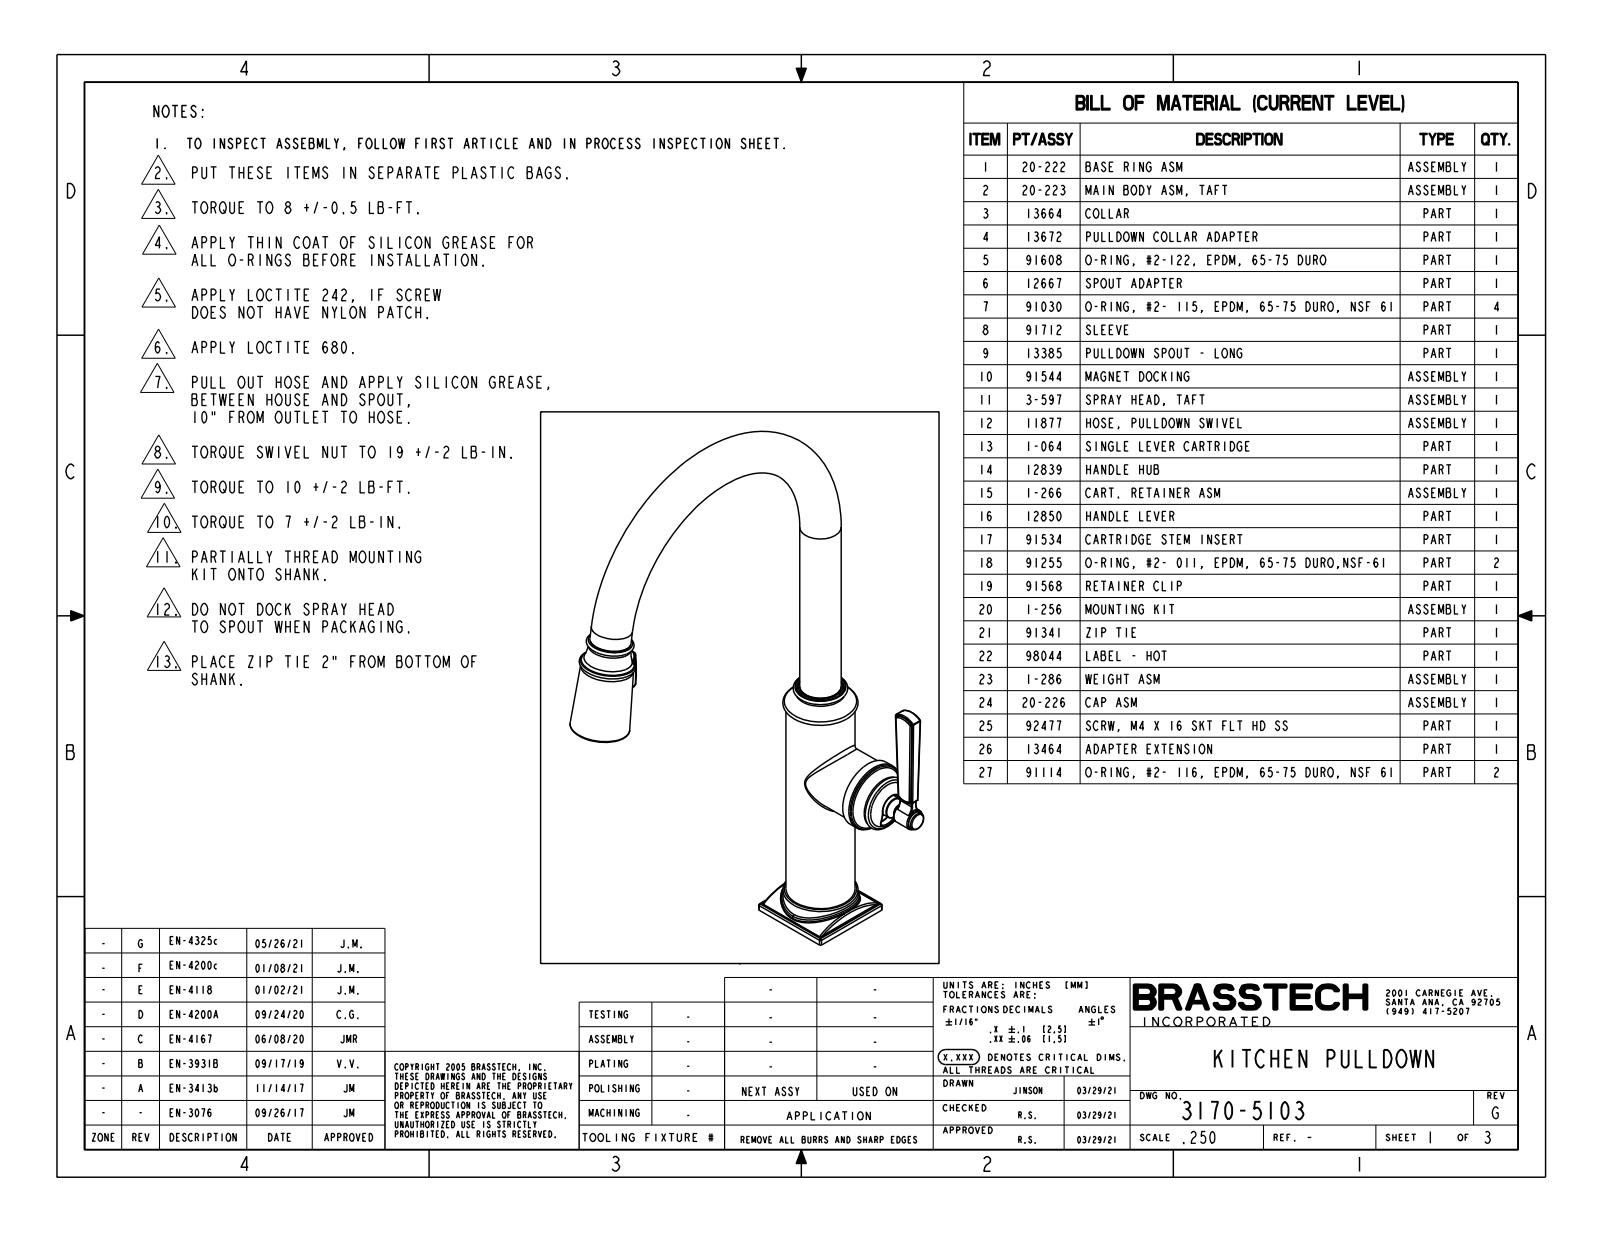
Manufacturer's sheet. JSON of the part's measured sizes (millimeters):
{"part_name": "3170-5103", "step_written_by": "CREO PARAMETRIC BY PTC INC, 2018400 (CONFIG_CONTROL_DESIGN)", "units": "millimeters", "bodies": {"solids": 2, "faces": 498, "planar": 76, "cylindrical": 73, "other": 349}, "overall_size": [437.8, 268, 126.7], "volume_mm3": 818900, "surface_area_mm2": 101100, "round_holes": [[12.5, 1], [31.5, 1]], "round_bosses_or_shafts": [[52.5, 1], [50, 1], [48.3, 1], [45.7, 1], [31.2, 1], [28.5, 1], [15.1, 1], [15, 1]], "partial_cylinders_radius": [[0.5, 10], [0.6, 8], [1, 8], [0.2, 4], [0.8, 4], [1.5, 4], [2.5, 2], [8.3, 2]], "face_to_face_distances": [193, 193.5, 0.5, 61.5, 2, 59.4, 77.7, 16.3, 18.3, 57.4]}
